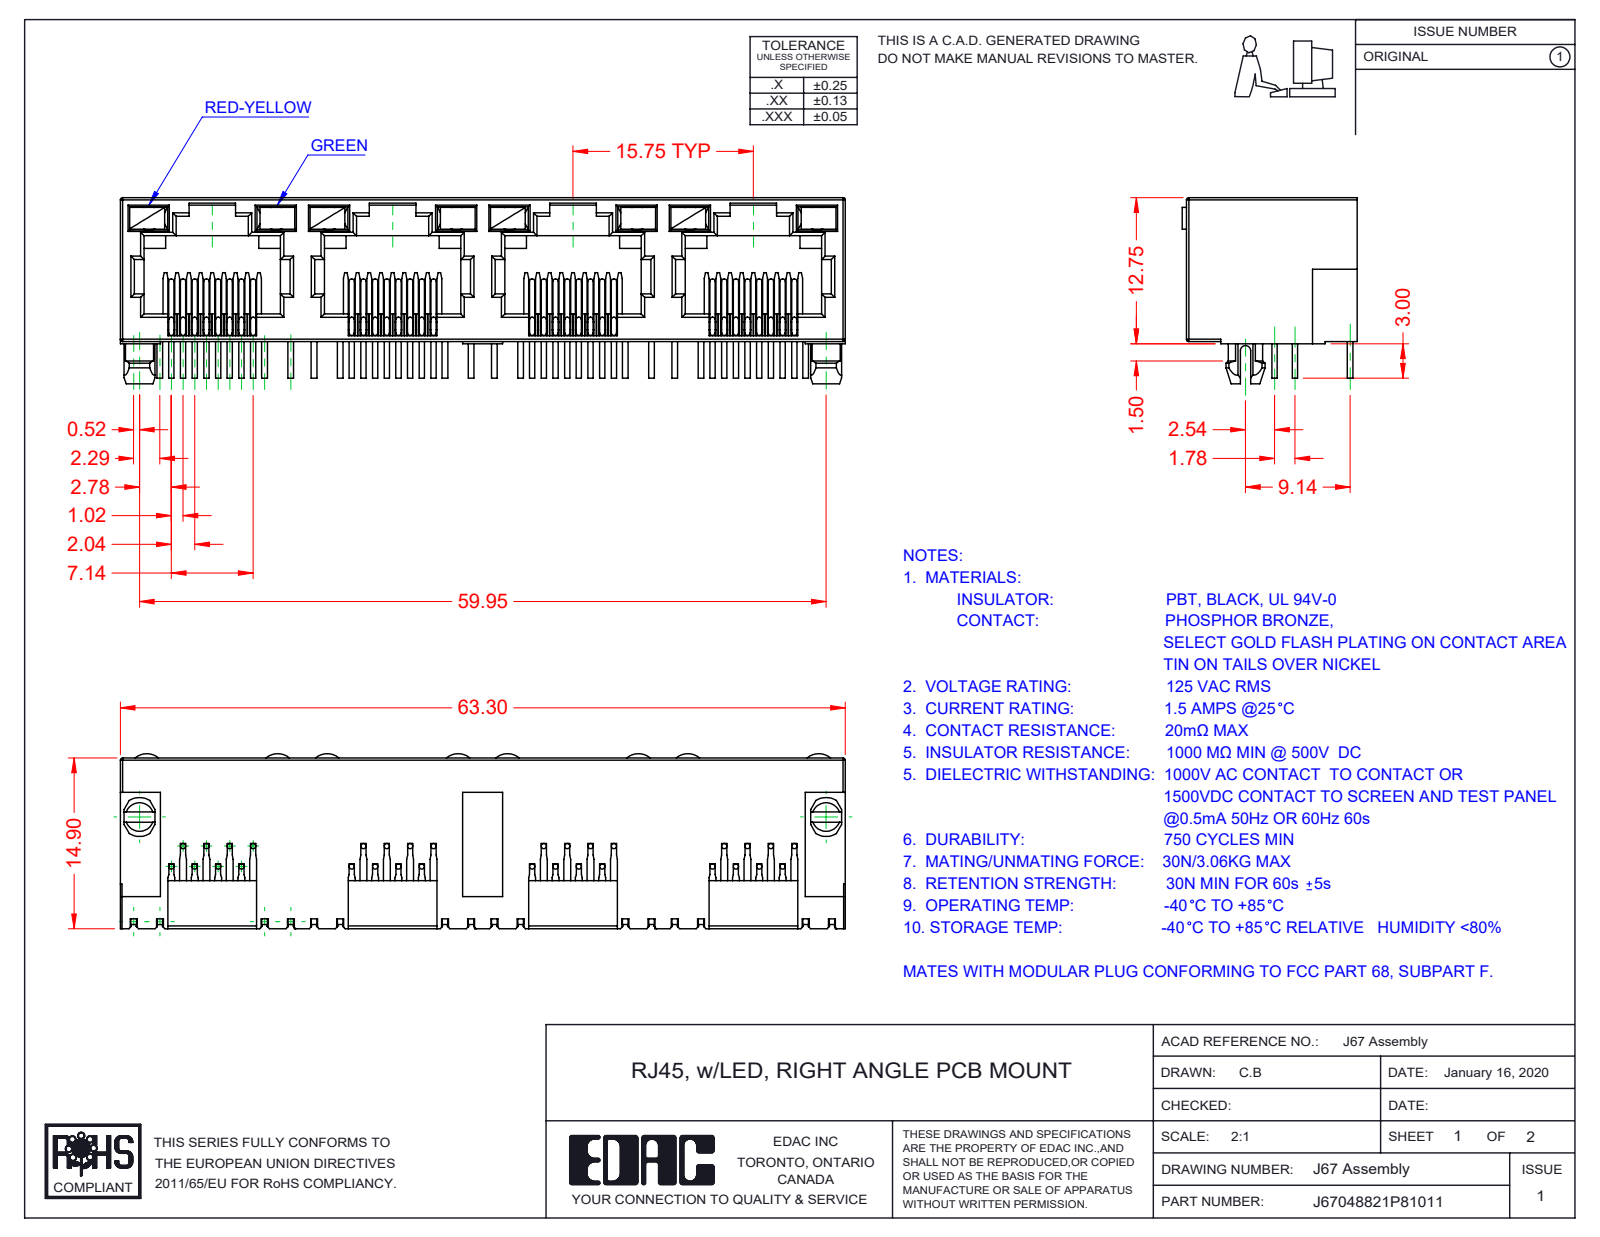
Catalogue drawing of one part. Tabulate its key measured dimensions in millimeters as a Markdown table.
| quantity | value |
| --- | --- |
| part name | 67 Insulator; 67 LED LH_8-Red-Yellow; 67 Contacts; 67 LED RH_3-Green (+1 more) |
| STEP written by | SolidWorks 2016 (CONFIG_CONTROL_DESIGN) |
| units | millimeters |
| bodies | 41 solids, 2473 faces (1781 planar, 484 cylindrical, 208 other) |
| overall size | 63.3 × 16.25 × 15.28 |
| volume | 5 159 mm³ |
| surface area | 11 573 mm² |
| round bosses / shafts (diameter × count) | 0.46 × 96 |
| partial cylindrical surfaces (radius × count) | 0.2 × 66, 0.3 × 29, 0.45 × 9, 1.55 × 8, 1.5 × 2, 1.7 × 2, 0.35 × 1, 1 × 1 |
| main face-to-face distances | 0.5, 12.55, 1.89, 0.89, 10, 15.75, 1, 1.39, 11, 11.89 |
